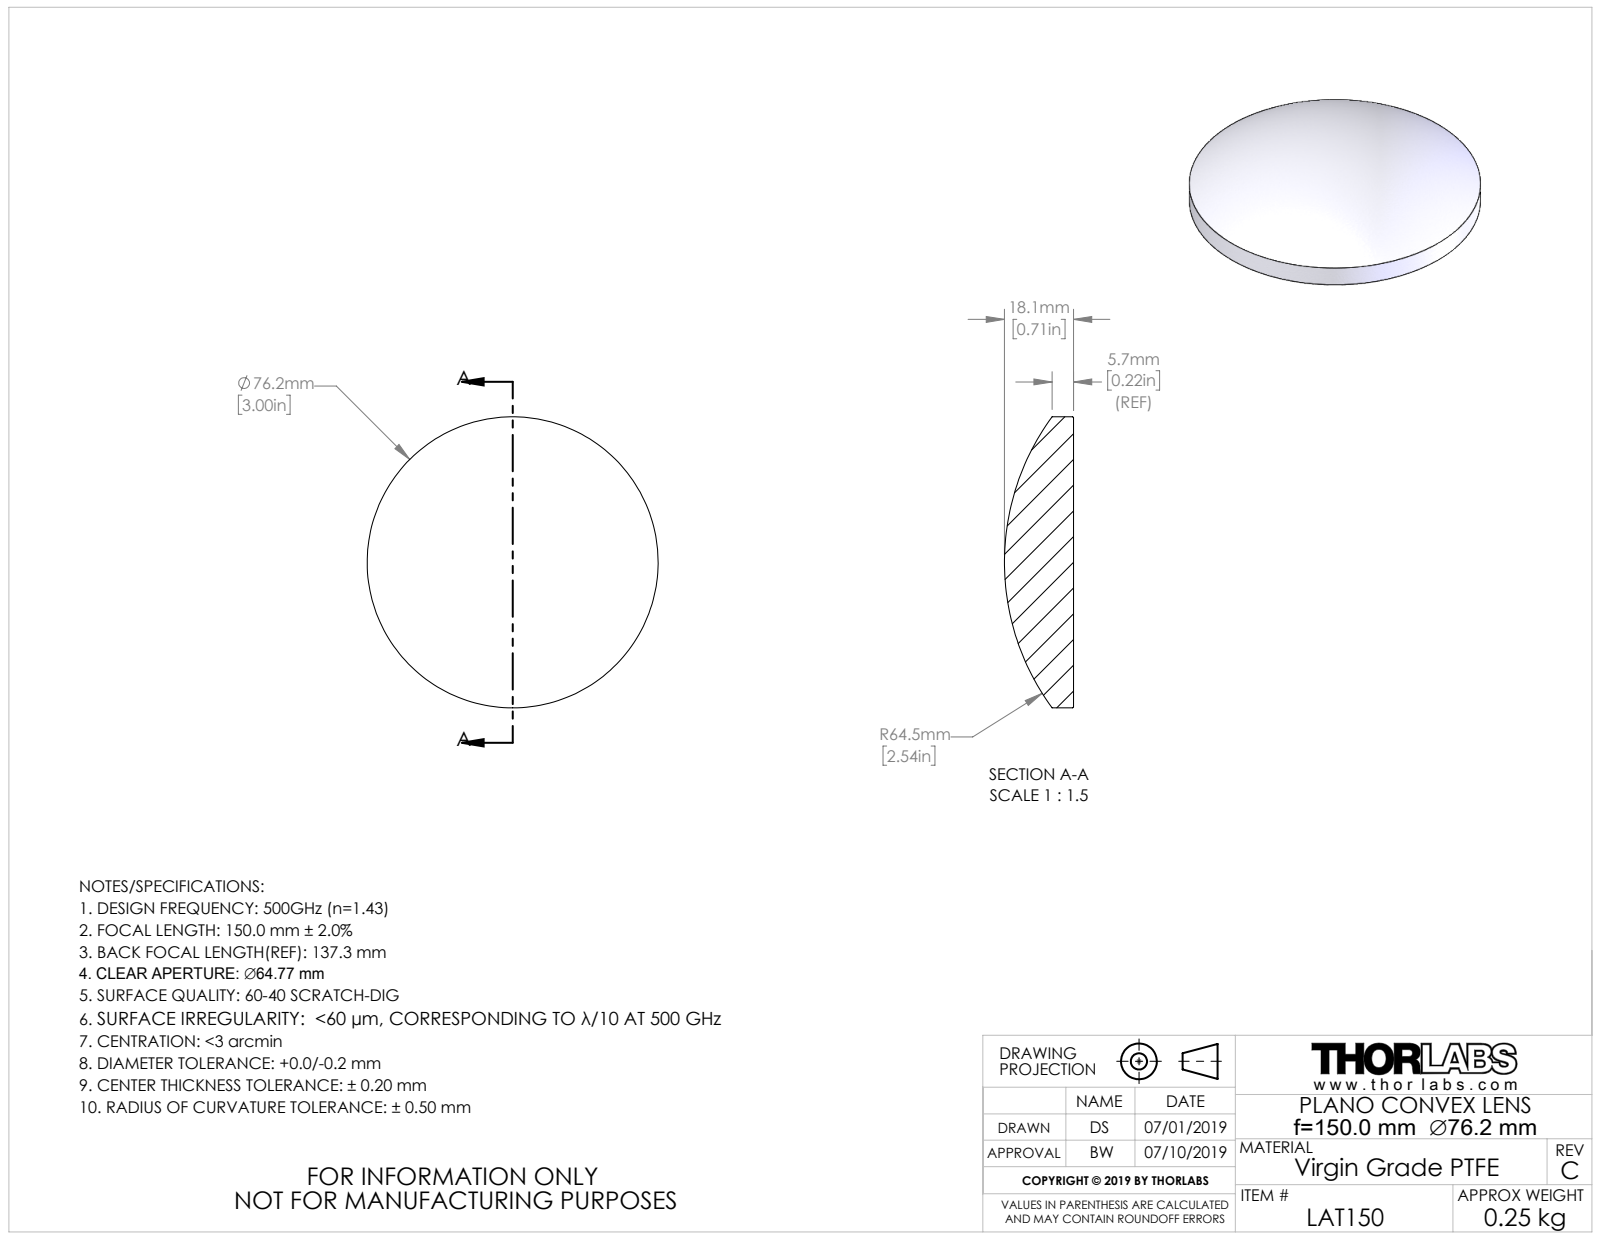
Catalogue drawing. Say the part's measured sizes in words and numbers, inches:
The part is named "TTN041007-E0W". Its 3-D file was written by "SolidWorks 2018 (CONFIG_CONTROL_DESIGN)". It is 1 solid with 7 faces: 1 planar, 2 cylindrical and 4 other. Overall it measures 3 by 3 by 0.713 inches. Its volume is 3.367 cubic inches and its surface area 16.94 square inches. Round bosses or shafts: 1 of diameter 3.
